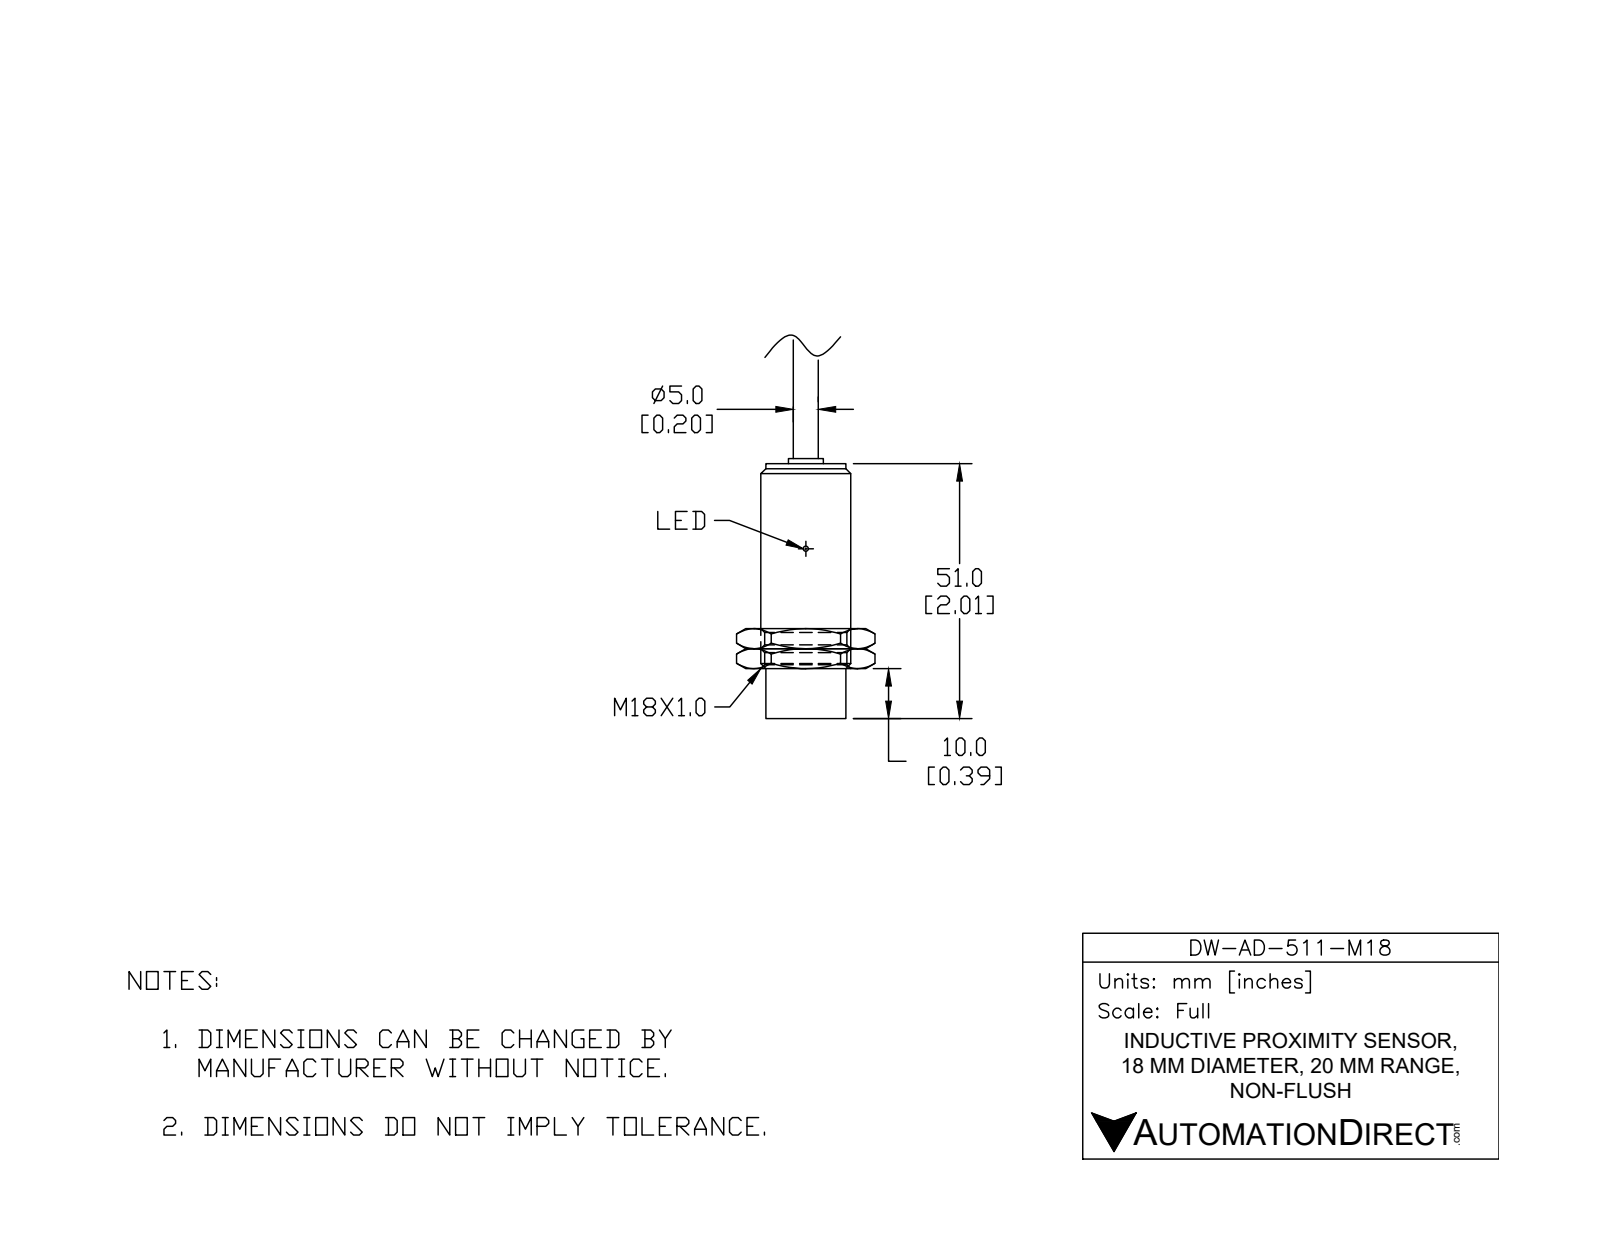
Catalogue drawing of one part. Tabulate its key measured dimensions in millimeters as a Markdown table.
| quantity | value |
| --- | --- |
| part name | DW-AD-511-M18 |
| STEP written by | SolidWorks 2017 (AUTOMOTIVE_DESIGN) |
| units | millimeters |
| bodies | 2 solids, 37 faces (18 planar, 7 cylindrical, 12 other) |
| overall size | 76.6 × 18 × 18 |
| volume | 13 200 mm³ |
| surface area | 3 815 mm² |
| round bosses / shafts (diameter × count) | 18 × 1, 16.5 × 1, 16.4 × 1, 10.5 × 1, 6.8 × 1, 5 × 1, 3 × 1 |
| main face-to-face distances | 51, 0.8, 53, 2, 51.8, 1.2, 48, 3, 3.8, 5 |
